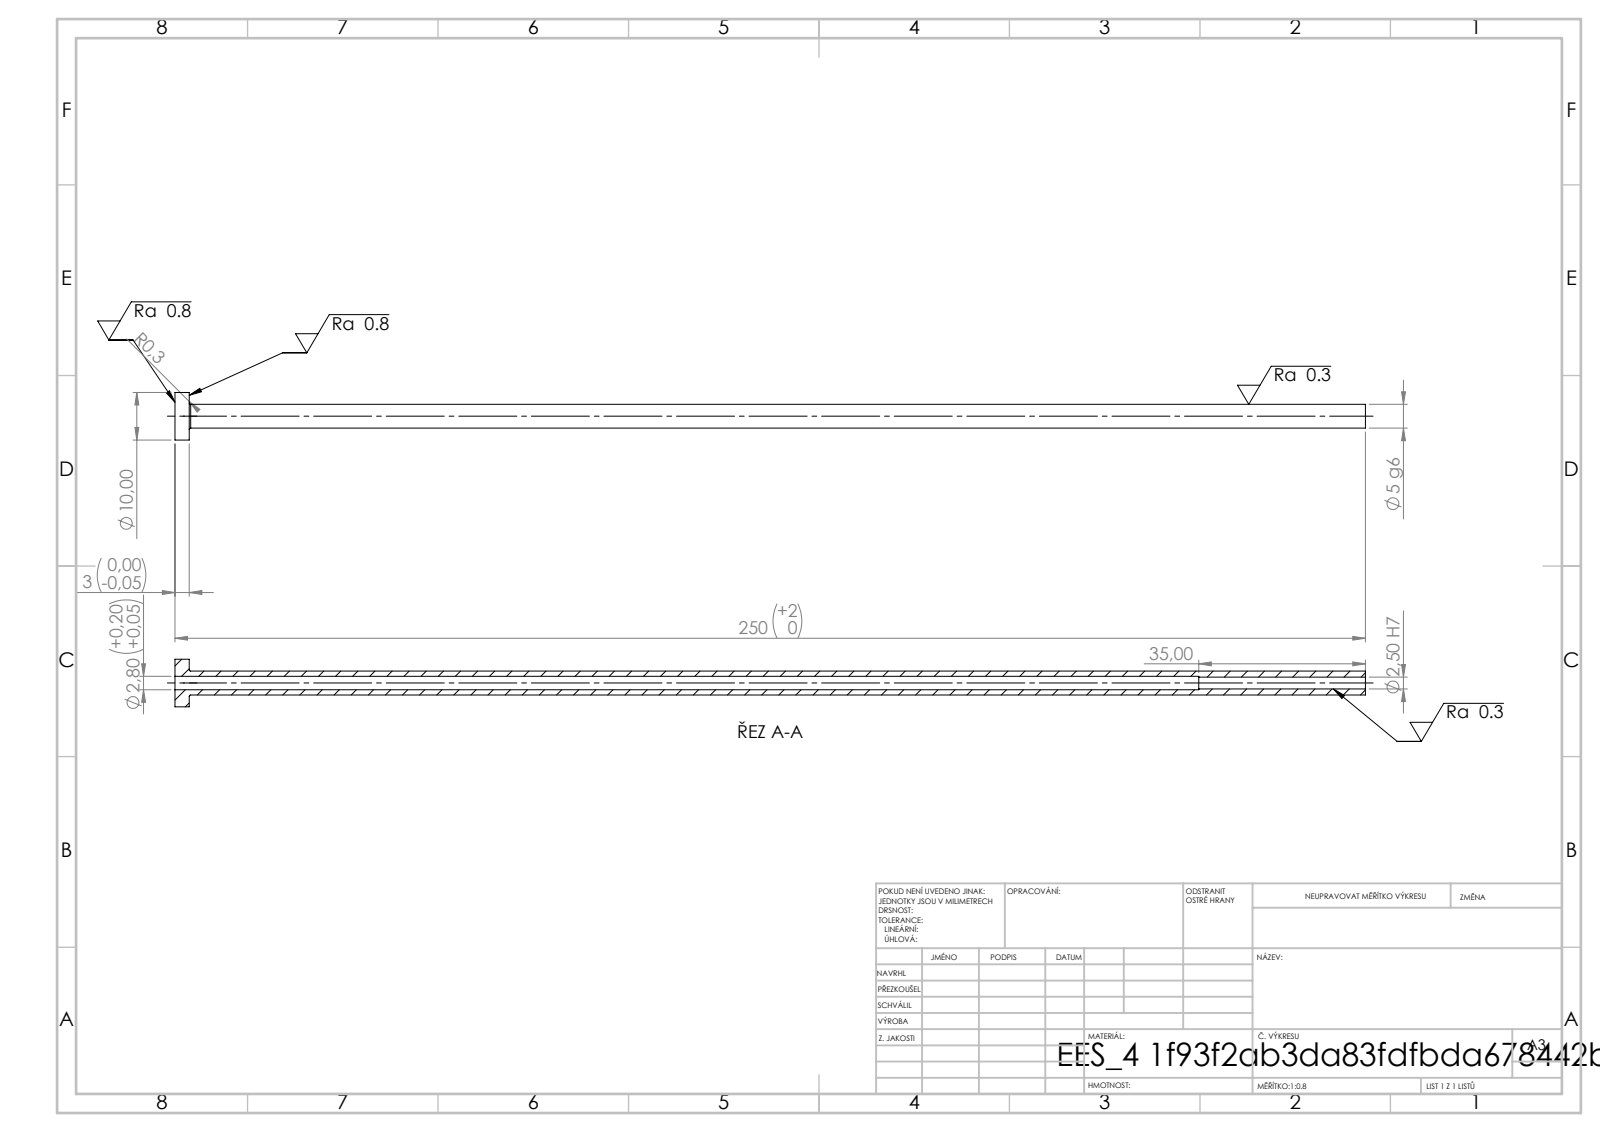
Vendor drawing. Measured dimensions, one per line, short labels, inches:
written by: SolidWorks 2019 (CONFIG_CONTROL_DESIGN)
unit: in
bodies: 1 solid, 14 faces (4 planar, 8 cylindrical, 2 other)
size: 9.843 × 0.394 × 0.394
volume: 0.219 in³; area: 9.743 in²
holes: 1× ⌀0.098, 1× ⌀0.11
bosses: 1× ⌀0.394, 1× ⌀0.197
face distances: 0.118, 9.843, 9.724, 8.465, 8.346, 1.378
